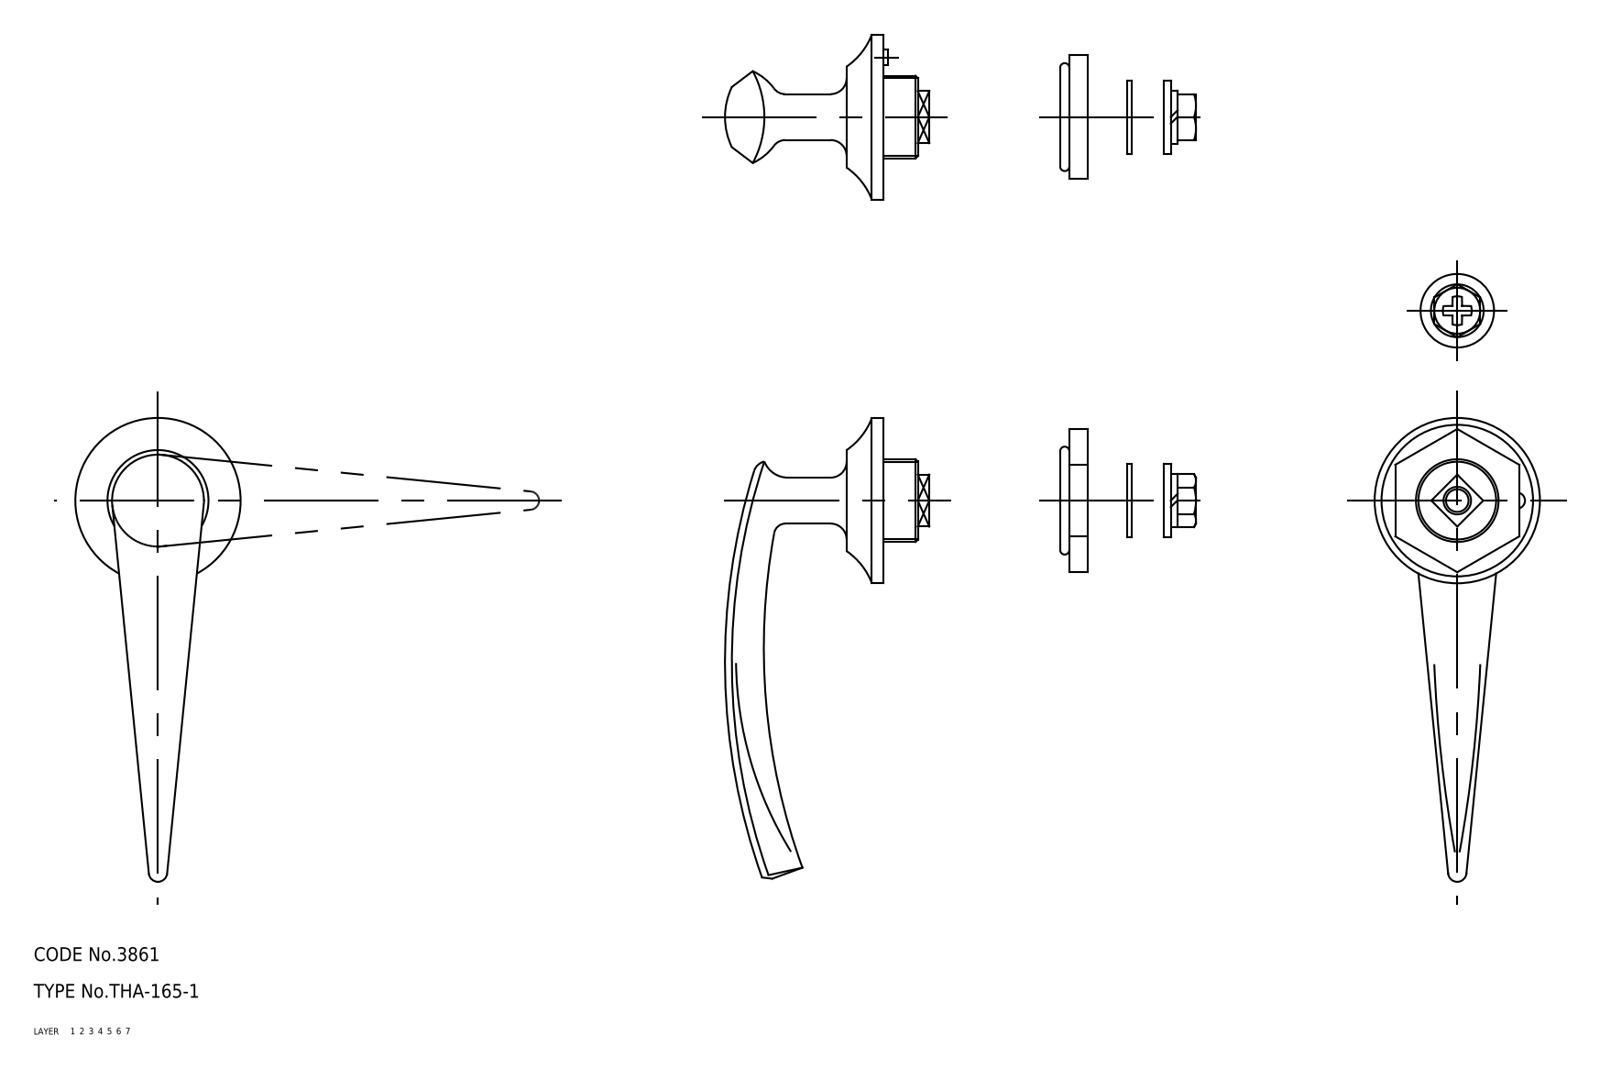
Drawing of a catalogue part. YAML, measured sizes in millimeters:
part_name: "washer_C; washer_B; washer_A; nut (+4 more)"
step_written_by: "CADfix (AUTOMOTIVE_DESIGN)"
units: millimeters
bodies: {solids: 7, faces: 133, planar: 0, cylindrical: 0, other: 133}
overall_size: [101, 51.6, 36]
volume: 17392
surface_area: 11509
